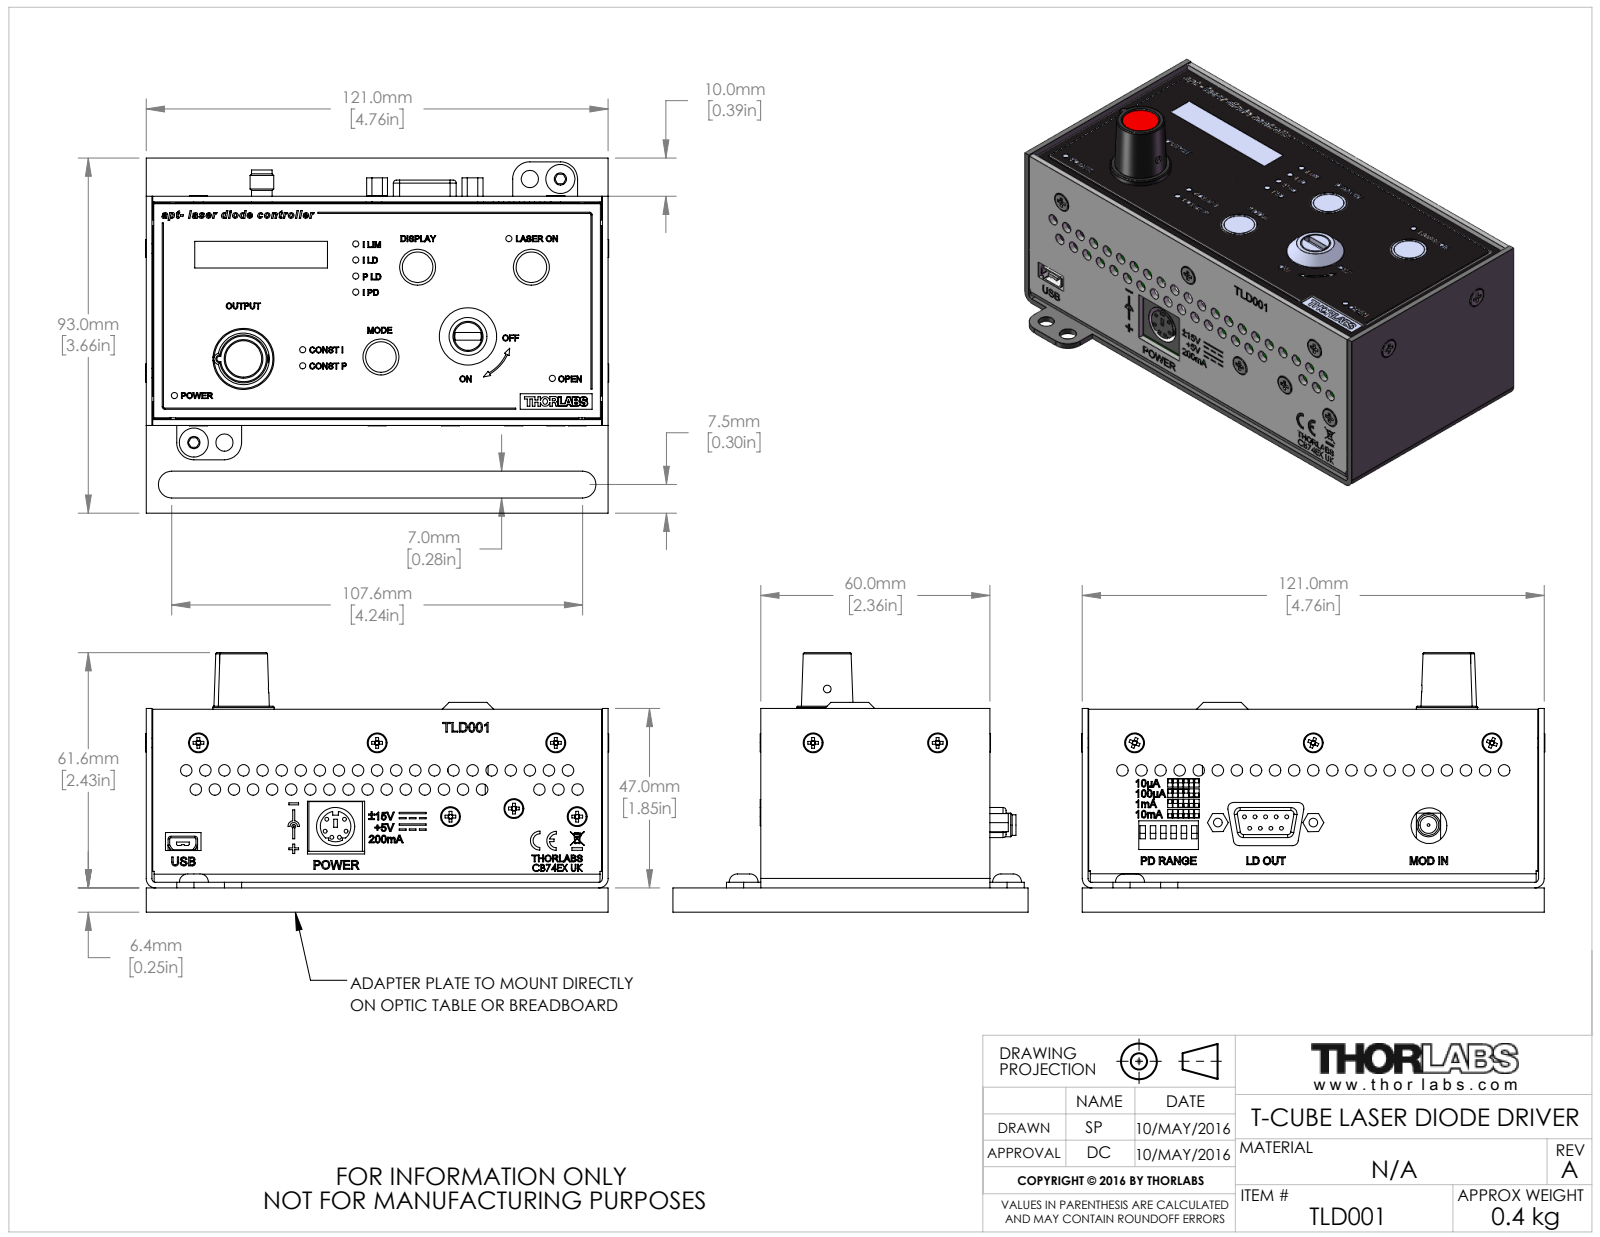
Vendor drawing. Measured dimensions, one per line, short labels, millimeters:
name: TLD001
written by: SolidWorks 2016 (AUTOMOTIVE_DESIGN)
unit: mm
bodies: 0 solids, 1321 faces (817 planar, 284 cylindrical, 220 other)
size: 121.3 × 93 × 67.95
holes: 40× ⌀3, 15× ⌀1, 2× ⌀2.26, 2× ⌀3.3, 2× ⌀4.5, 1× ⌀0.7, 1× ⌀1.02, 1× ⌀2, 1× ⌀4.4, 1× ⌀7.9, 1× ⌀9.35, 1× ⌀10
bosses: 8× ⌀4.7, 1× ⌀16, 1× ⌀15, 1× ⌀13.5, 1× ⌀12, 1× ⌀7.3, 1× ⌀6.2, 1× ⌀6
rounds: 7× R1.5, 6× R0.3, 5× R0.8, 4× R1.6, 4× R2.5, 4× R4.5, 3× R0.7, 3× R1
face distances: 1.5, 44, 6.35, 58.5, 7.85, 45.5, 15.95, 9.6, 8.1, 52.15
hole spacings: 5, 10, 15, 20, 5.59, 9.01, 25, 13.46
